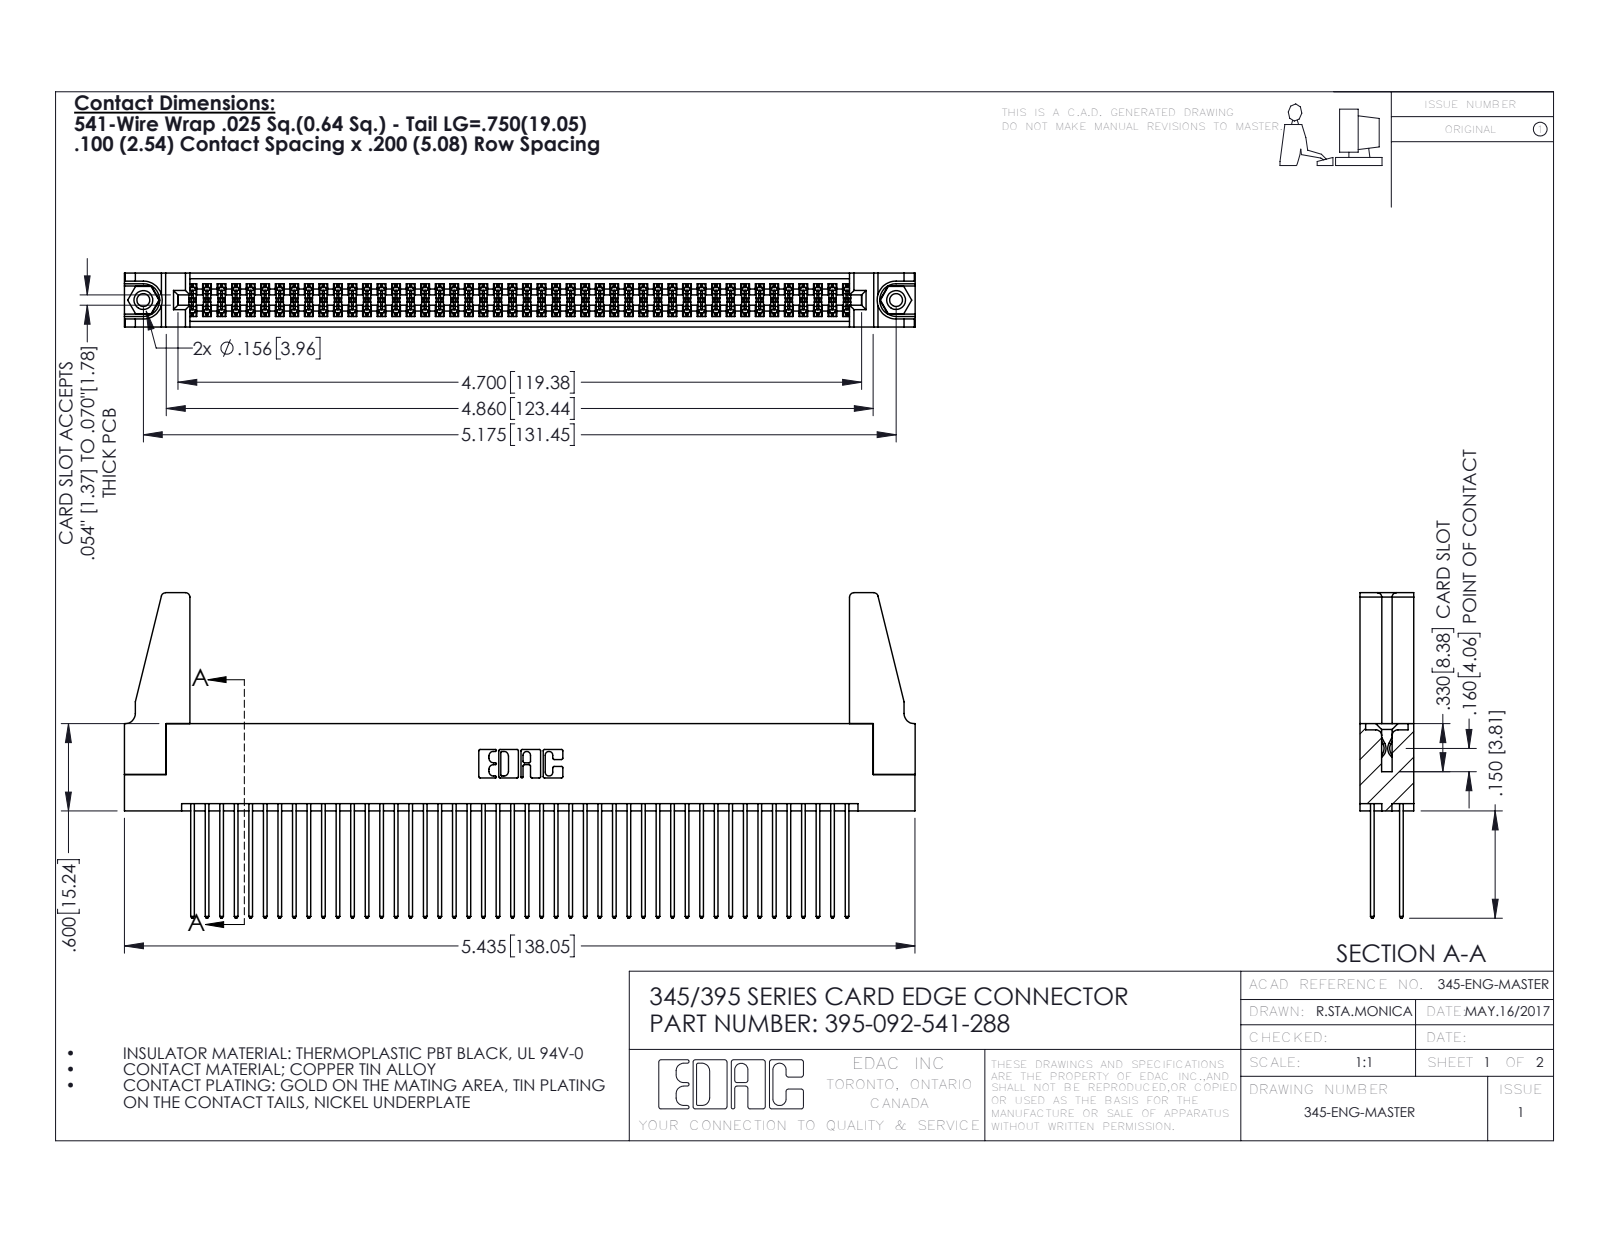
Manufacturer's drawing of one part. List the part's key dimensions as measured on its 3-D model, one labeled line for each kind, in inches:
Part name (STEP PRODUCT): 345 Part_Flush Mounting Lugs - 0.156 Dia-TH; 345-220-078_345-220-088; 345-250-001_345-250-001-102; 395-092-541-288 (+1 more)
STEP written by: SolidWorks 2016 (CONFIG_CONTROL_DESIGN)
Units: inches
Bodies: 97 solids, 4850 faces (3188 planar, 1646 cylindrical, 16 other)
Overall size (bounding box): 5.436 × 2.237 × 0.37
Volume: 1.051 in³ · Surface area: 40.83 in²
Round holes (diameter × count): ⌀0.089 ×2, ⌀0.125 ×2, ⌀0.156 ×2, ⌀0.064 ×1
Round bosses / shafts (diameter × count): ⌀0.155 ×2
Partial cylindrical surfaces — rounded edges, fillets, slot ends (radius × count): R0.006 ×138, R0.01 ×92, R0.01 ×22, R0.03 ×8, R0.007 ×6, R0.031 ×6, R0.026 ×3, R0.014 ×2
Main face-to-face distances: 0.072, 0.298, 0.2, 0.098, 0.272, 0.025, 0.37, 0.225, 0.175, 0.149
Hole centre spacings: 0.27, 4.939, 5.175
